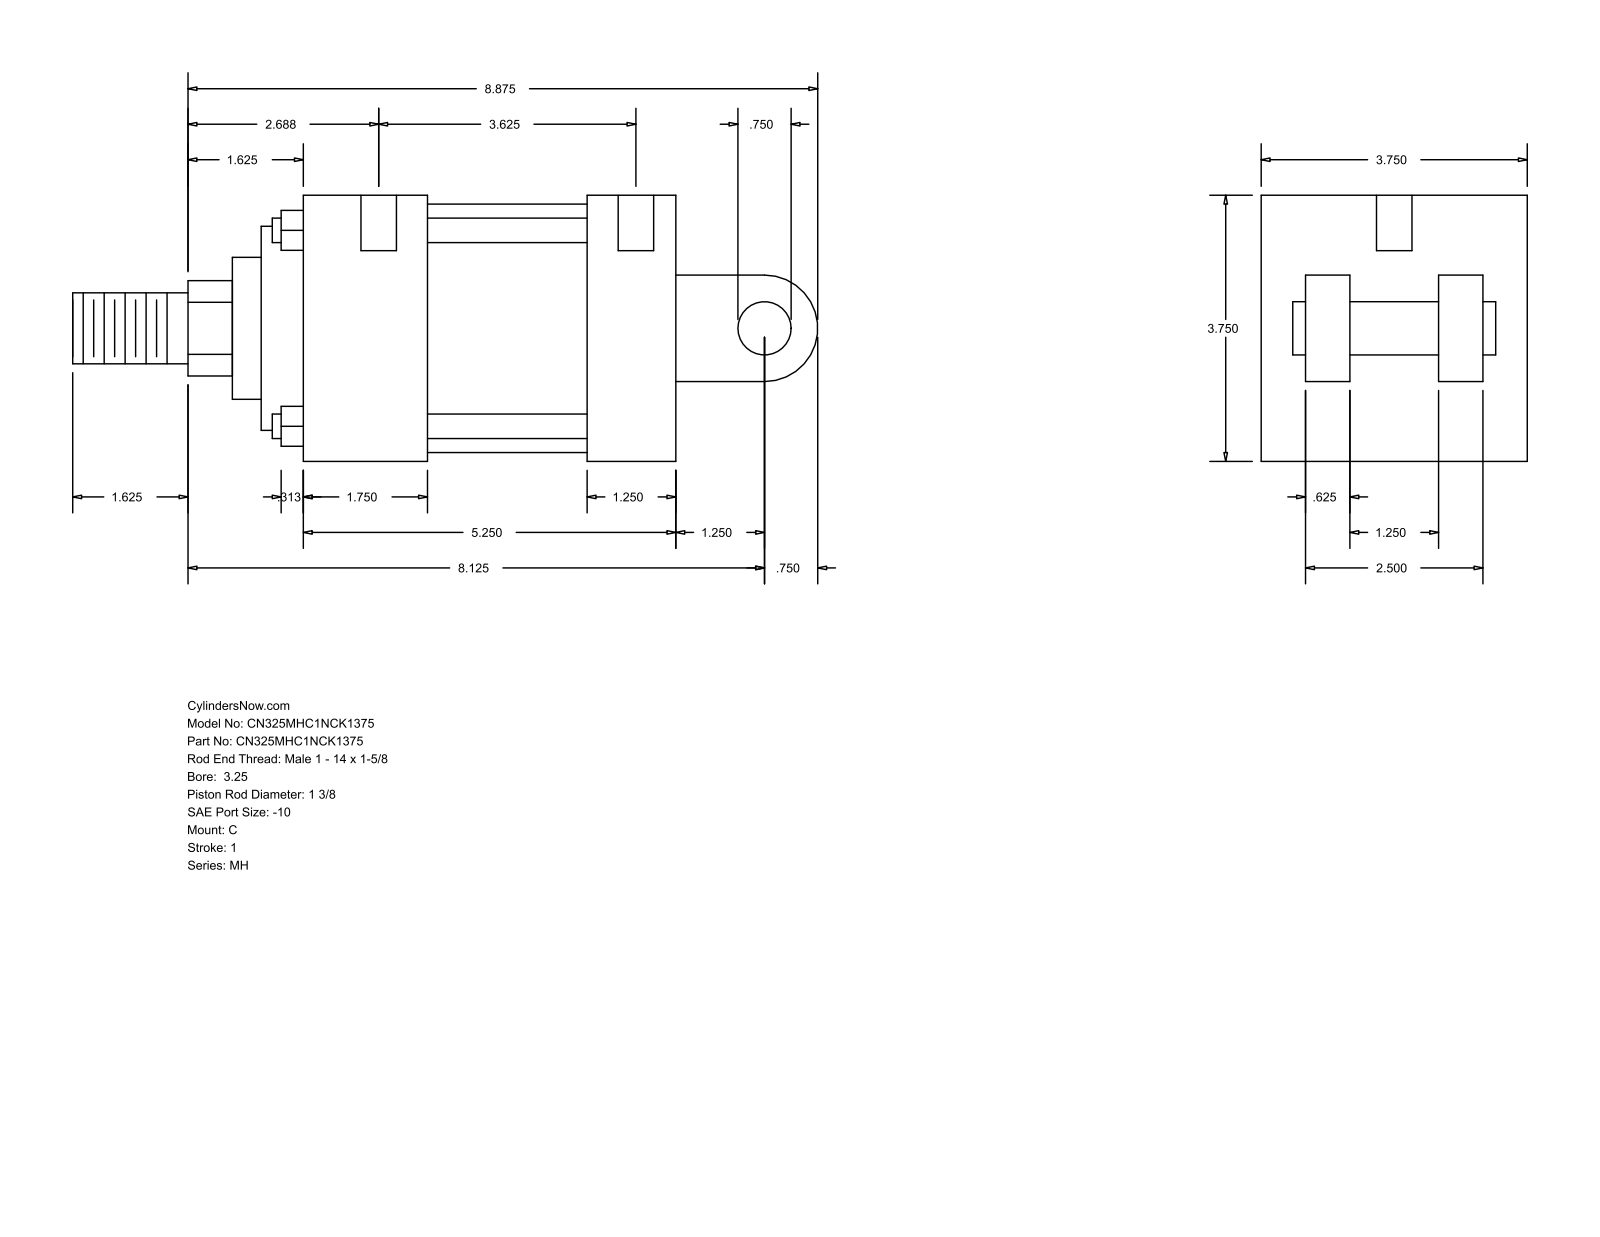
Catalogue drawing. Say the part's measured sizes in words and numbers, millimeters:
The part is named "MH_C__0325_1.375". Its 3-D file was written by "GSSL Pune (CONFIG_CONTROL_DESIGN)". It is 0 solids with 101 faces: 71 planar, 30 cylindrical and 0 other. Overall it measures 266.7 by 95.25 by 95.25 millimeters. Round holes: 4 of diameter 5.56, 2 of diameter 12.7. Round bosses or shafts: 4 of diameter 8.76, 1 of diameter 88.9, 1 of diameter 73.03, 1 of diameter 50.8, 1 of diameter 34.92, 1 of diameter 25.4, 1 of diameter 19.05. Partial cylindrical surfaces (rounded edges, fillets, slot ends): 1 of radius 17.06, 1 of radius 19.05. The main face-to-face distances are 95.24, 15.87, 31.74, 63.5, 133.35, 79.37, 47.63, 44.45, 101.61, 57.16. The hole center spacings are 98.43, 1.59, 4.76, 92.08, 93.67, 96.84.
